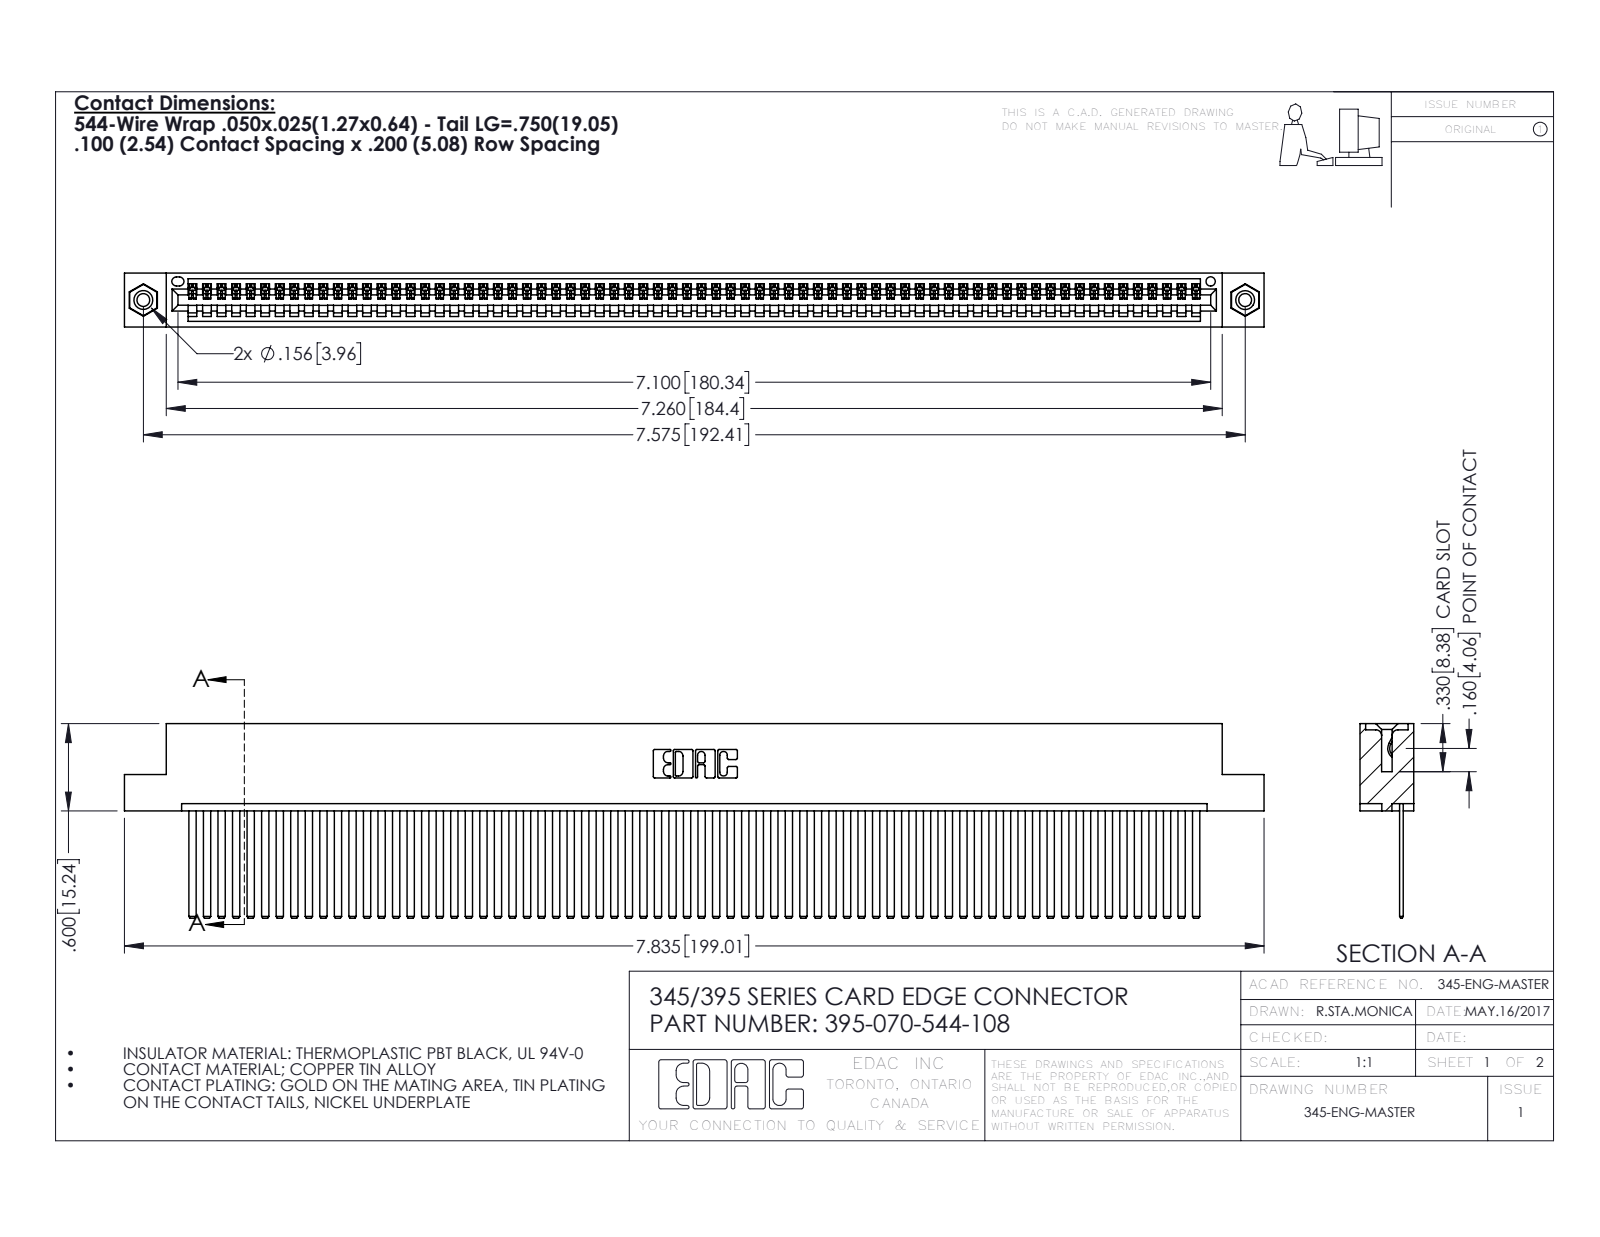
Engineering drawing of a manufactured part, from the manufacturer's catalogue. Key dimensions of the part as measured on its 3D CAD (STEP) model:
Part name (STEP PRODUCT): 345 Part_Flush Mounting Lugs - 0.156 Dia-TI; 395-070-544-108; 345-250-001_345-250-003-102; 345-292-001_345-293-144
STEP written by: SolidWorks 2016 (CONFIG_CONTROL_DESIGN)
Units: inches
Bodies: 73 solids, 3826 faces (2632 planar, 1178 cylindrical, 16 other)
Overall size (bounding box): 7.835 × 1.337 × 0.37
Volume: 1.217 in³ · Surface area: 45.46 in²
Round holes (diameter × count): ⌀0.089 ×2, ⌀0.125 ×2, ⌀0.156 ×2, ⌀0.064 ×1
Round bosses / shafts (diameter × count): ⌀0.155 ×2
Partial cylindrical surfaces — rounded edges, fillets, slot ends (radius × count): R0.006 ×140, R0.01 ×22, R0.007 ×6, R0.031 ×6, R0.026 ×3, R0.031 ×2, R0.04 ×2, R0.014 ×1
Main face-to-face distances: 0.072, 0.298, 0.025, 0.098, 0.272, 0.37, 0.2, 0.225, 0.149, 0.072
Hole centre spacings: 0.27, 7.339, 7.575
